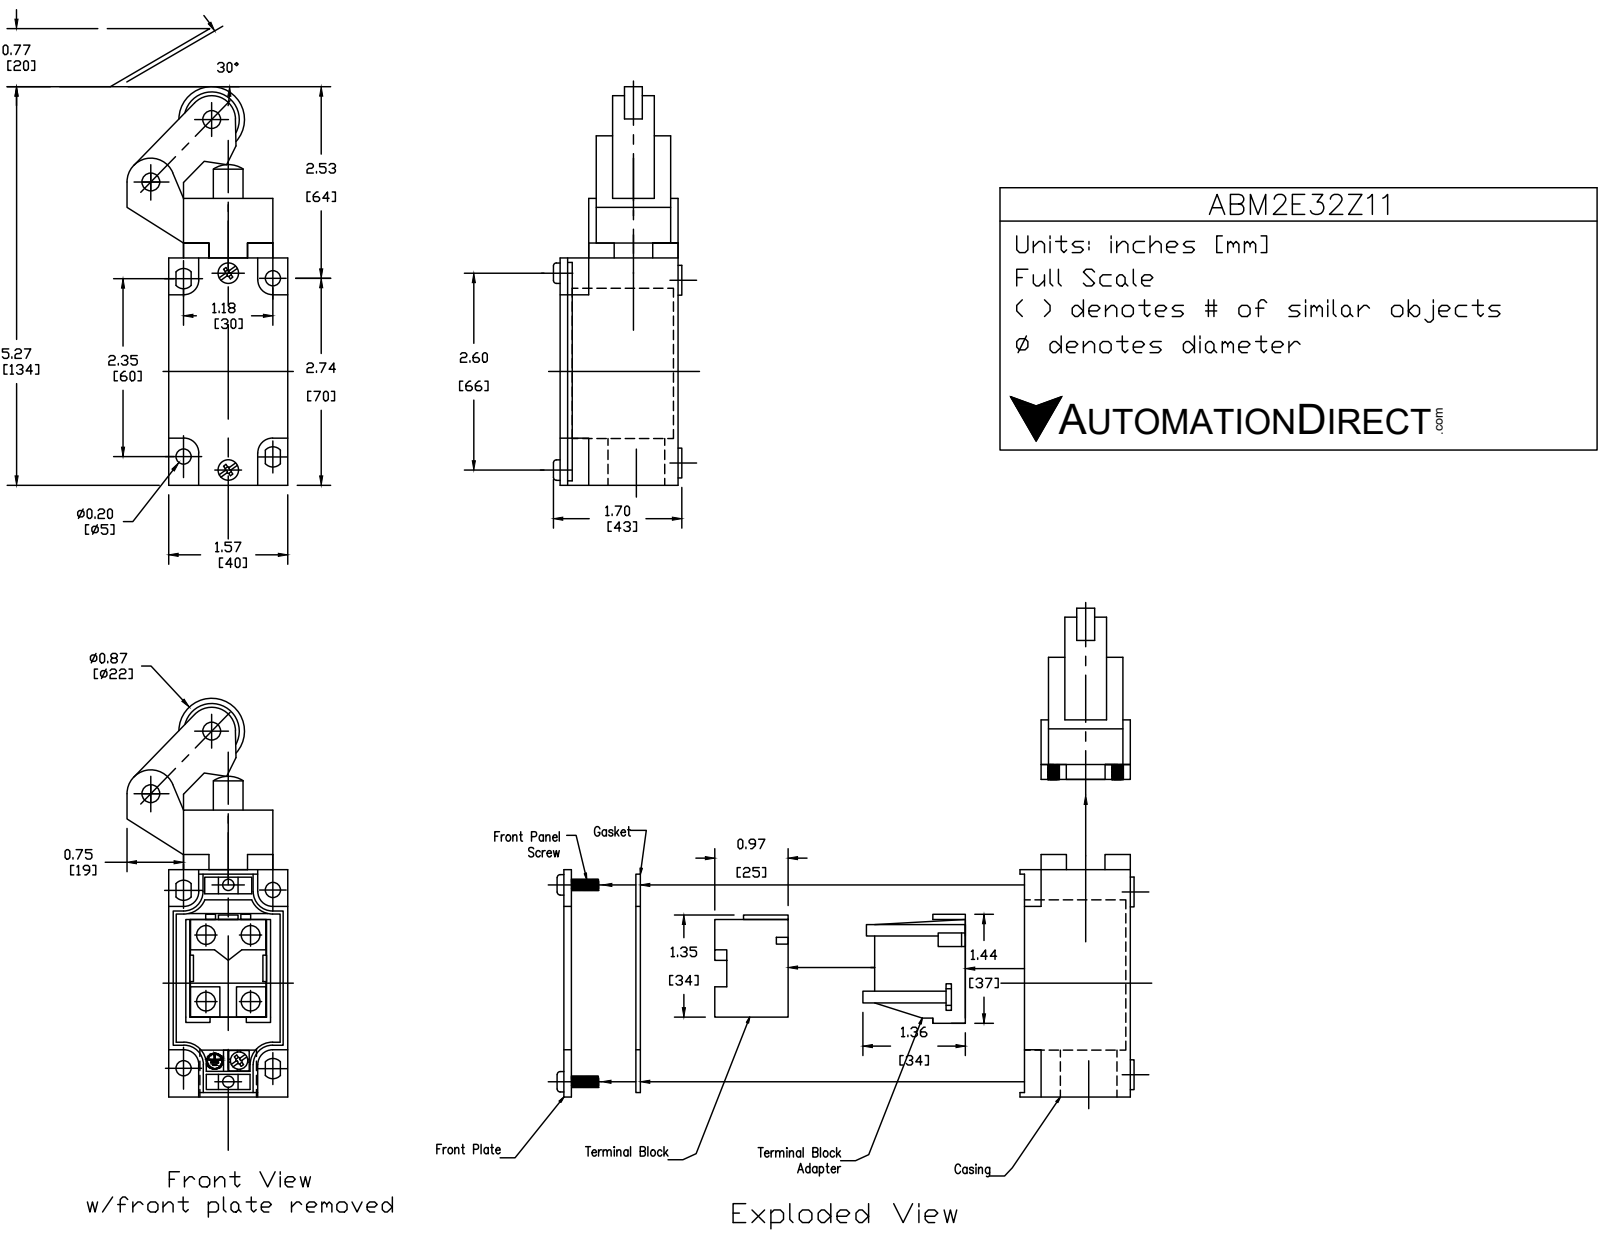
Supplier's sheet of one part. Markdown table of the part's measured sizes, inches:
| quantity | value |
| --- | --- |
| part name | ABM2E32Z11 |
| STEP written by | SolidWorks 2017 (AUTOMOTIVE_DESIGN) |
| units | inches |
| bodies | 4 solids, 221 faces (108 planar, 90 cylindrical, 23 other) |
| overall size | 5.287 × 2.126 × 1.705 |
| volume | 8.579 in³ |
| surface area | 50.73 in² |
| round holes (diameter × count) | 0.205 × 2, 0.394 × 1, 0.669 × 1, 0.748 × 1 |
| round bosses / shafts (diameter × count) | 0.394 × 5, 0.276 × 3, 0.866 × 1, 0.453 × 1 |
| partial cylindrical surfaces (radius × count) | 0.059 × 16, 0.039 × 5, 0.197 × 4, 0.128 × 2, 0.315 × 2, 0.472 × 2, 0.236 × 1, 0.453 × 1 |
| main face-to-face distances | 1.575, 0.325, 1.555, 0.118, 0.197, 0.738, 1.181, 0.856, 0.443, 0.413 |
| hole center spacings | 0.039, 2.641 |
